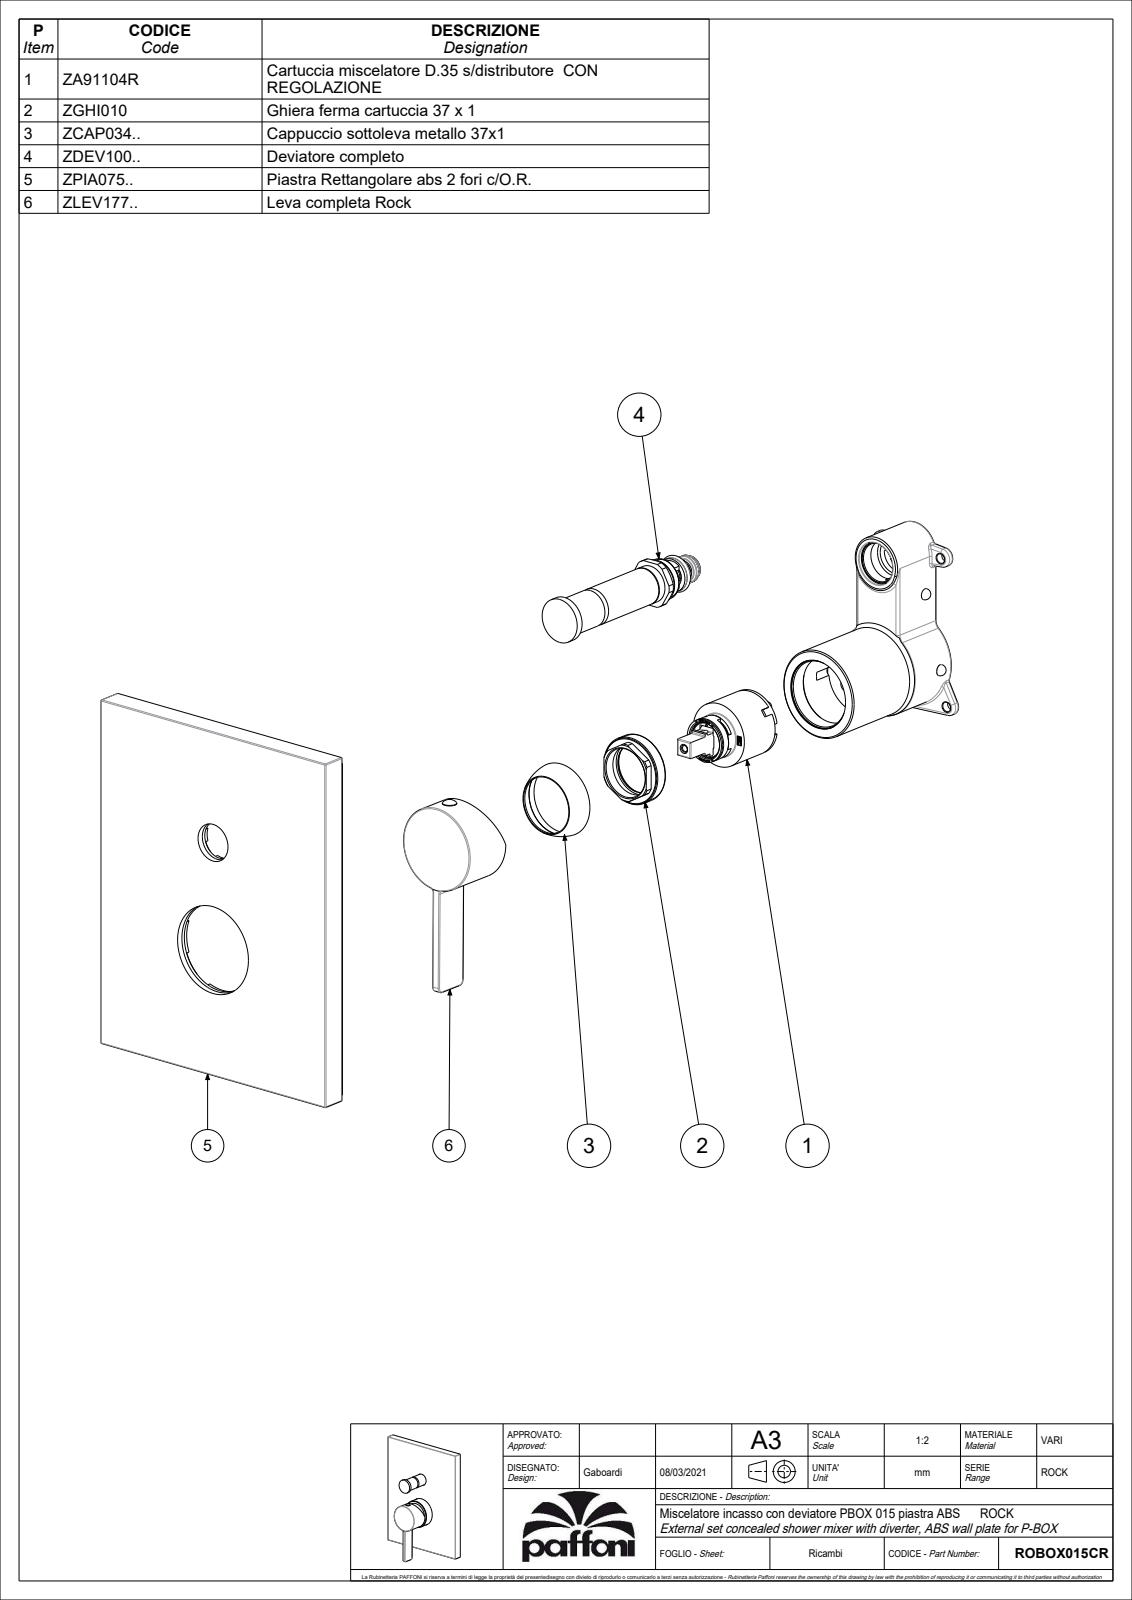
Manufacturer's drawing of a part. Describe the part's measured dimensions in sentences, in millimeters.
The part is named "ROBOX015CR". Its 3-D file was written by "CREO PARAMETRIC BY PTC INC, 2020044 (CONFIG_CONTROL_DESIGN)". It is 2 solids with 187 faces: 54 planar, 65 cylindrical and 68 other. Overall it measures 201.75 by 154 by 65.6 millimeters. Its volume is 450 842 cubic millimeters and its surface area 94 291 square millimeters. Round holes: 1 of diameter 3, 1 of diameter 4.2, 1 of diameter 5.5, 1 of diameter 30.6, 1 of diameter 36, 1 of diameter 37.5. Round bosses or shafts: 1 of diameter 48.1, 1 of diameter 45.5, 1 of diameter 24, 1 of diameter 20, 1 of diameter 15, 1 of diameter 7.6. Partial cylindrical surfaces (rounded edges, fillets, slot ends): 17 of radius 0.5, 2 of radius 0.3, 2 of radius 1.5, 2 of radius 2, 2 of radius 3, 1 of radius 3.5. The main face-to-face distances are 13.5, 154, 74.75, 79.25, 192, 4.5, 61.6, 48.1, 20, 33.5.
